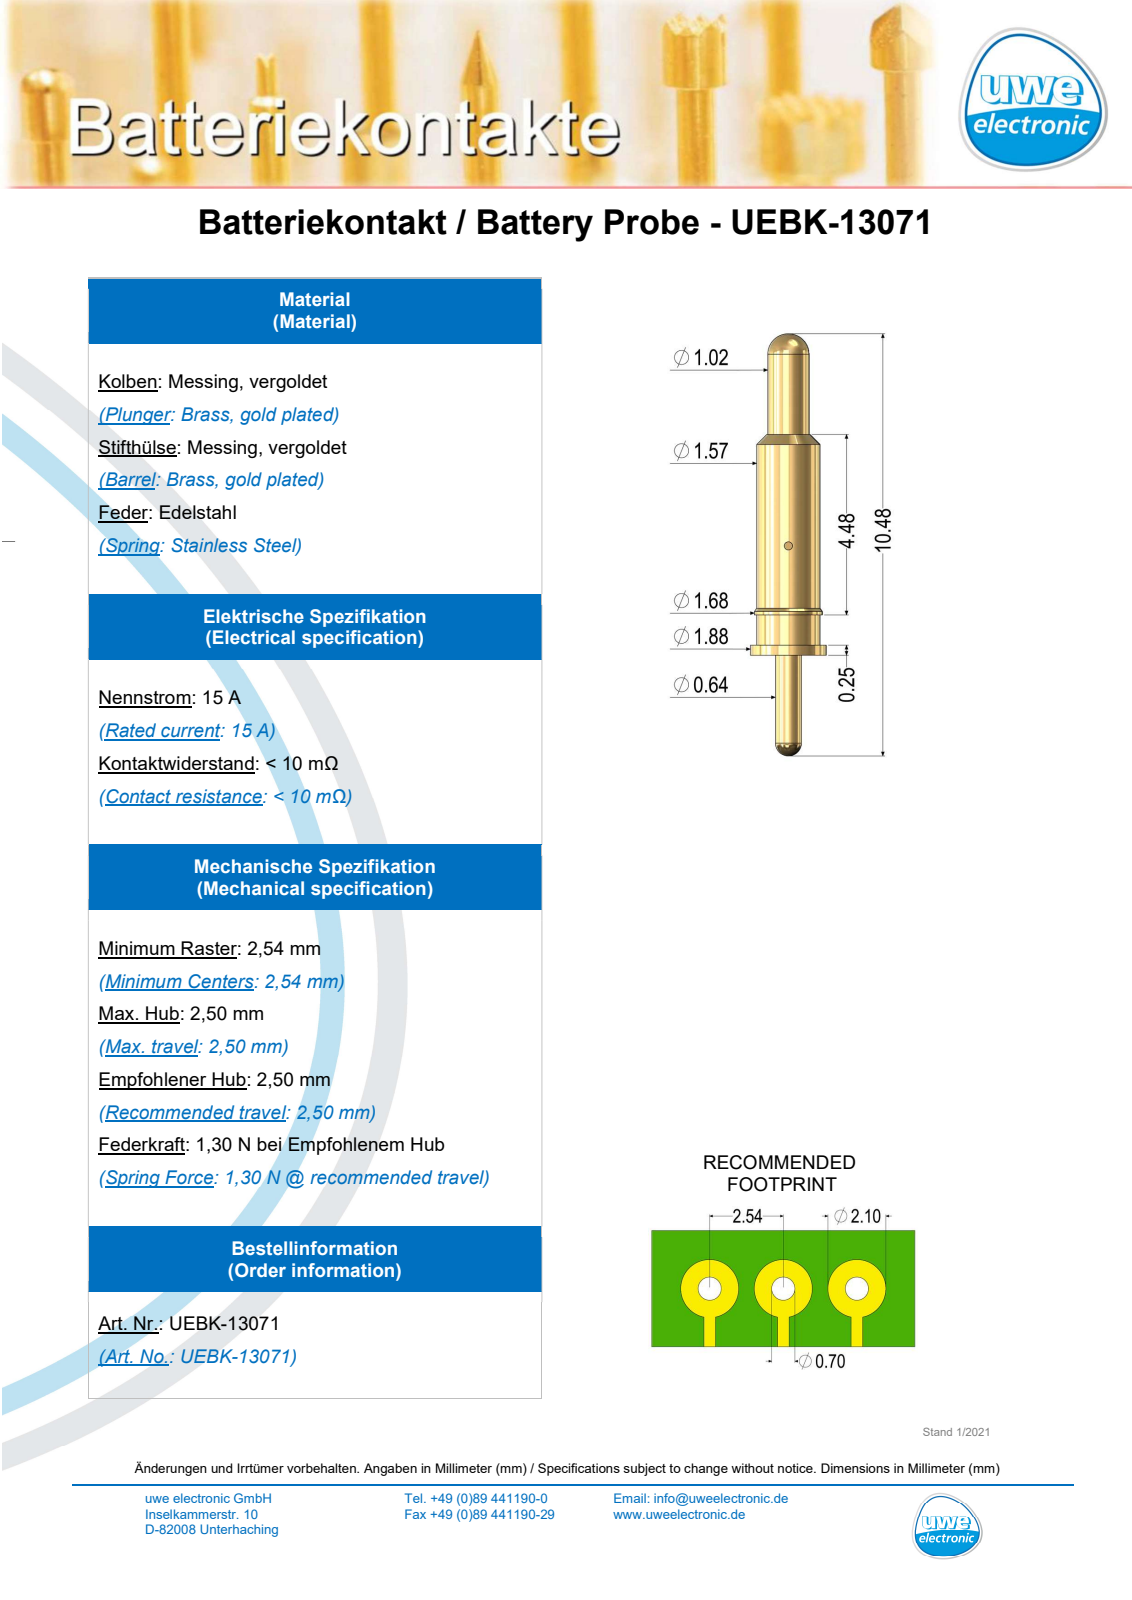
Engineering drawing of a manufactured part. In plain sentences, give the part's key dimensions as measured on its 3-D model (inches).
The part is named "UEBK-13071_2017_08_29". Its 3-D file was written by "SolidWorks 2017 (AUTOMOTIVE_DESIGN)". It is 1 solid with 27 faces: 5 planar, 14 cylindrical and 8 other. Overall it measures 0.413 by 0.074 by 0.074 inches. Its volume is 0.001 cubic inches and its surface area 0.07 square inches. Round holes: 1 of diameter 0.008. Round bosses or shafts: 1 of diameter 0.074, 1 of diameter 0.066, 1 of diameter 0.062, 1 of diameter 0.04, 1 of diameter 0.025. The main face-to-face distances are 0.03, 0.039, 0.176, 0.206, 0.216.
